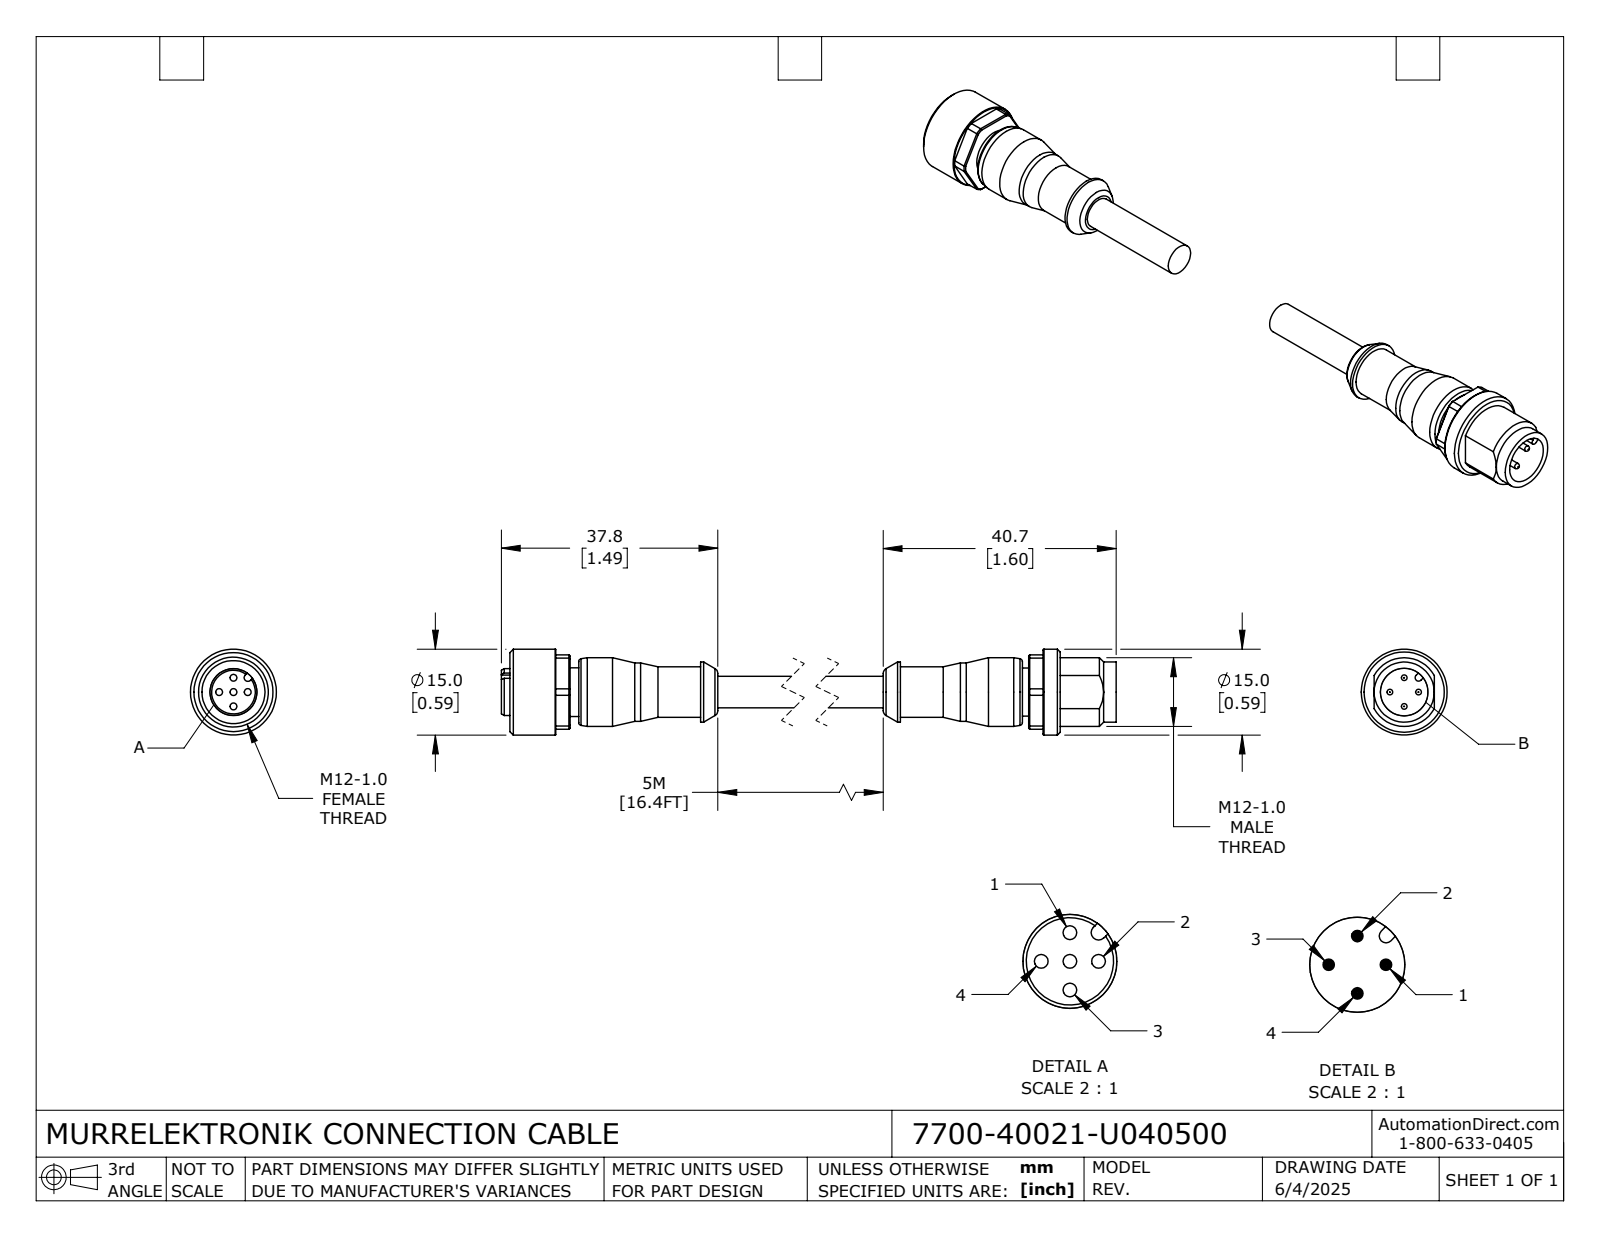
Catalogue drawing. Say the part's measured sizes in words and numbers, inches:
The part is named "7700-40021-U040500_MALE; 7700-40021-U040500_FEMALE; 7700-40021-U040500". Its 3-D file was written by "SolidWorks 2024 (CONFIG_CONTROL_DESIGN)". It is 2 solids with 191 faces: 59 planar, 71 cylindrical and 61 other. Overall it measures 5.65 by 0.591 by 0.591 inches. Its volume is 0.487 cubic inches and its surface area 7.972 square inches. Round holes: 5 of diameter 0.047, 1 of diameter 0.327, 1 of diameter 0.433. Round bosses or shafts: 4 of diameter 0.039, 1 of diameter 0.591, 1 of diameter 0.472, 1 of diameter 0.413, 1 of diameter 0.402, 1 of diameter 0.346, 1 of diameter 0.335, 1 of diameter 0.331. Partial cylindrical surfaces (rounded edges, fillets, slot ends): 1 of radius 0.024, 1 of radius 0.026, 1 of radius 0.283. The main face-to-face distances are 0.512, 0.118, 4.575, 0.413, 4.945, 0.472, 4.791, 0.295, 0.059, 0.098. The hole center spacings are 0.098, 0.139, 0.197.
